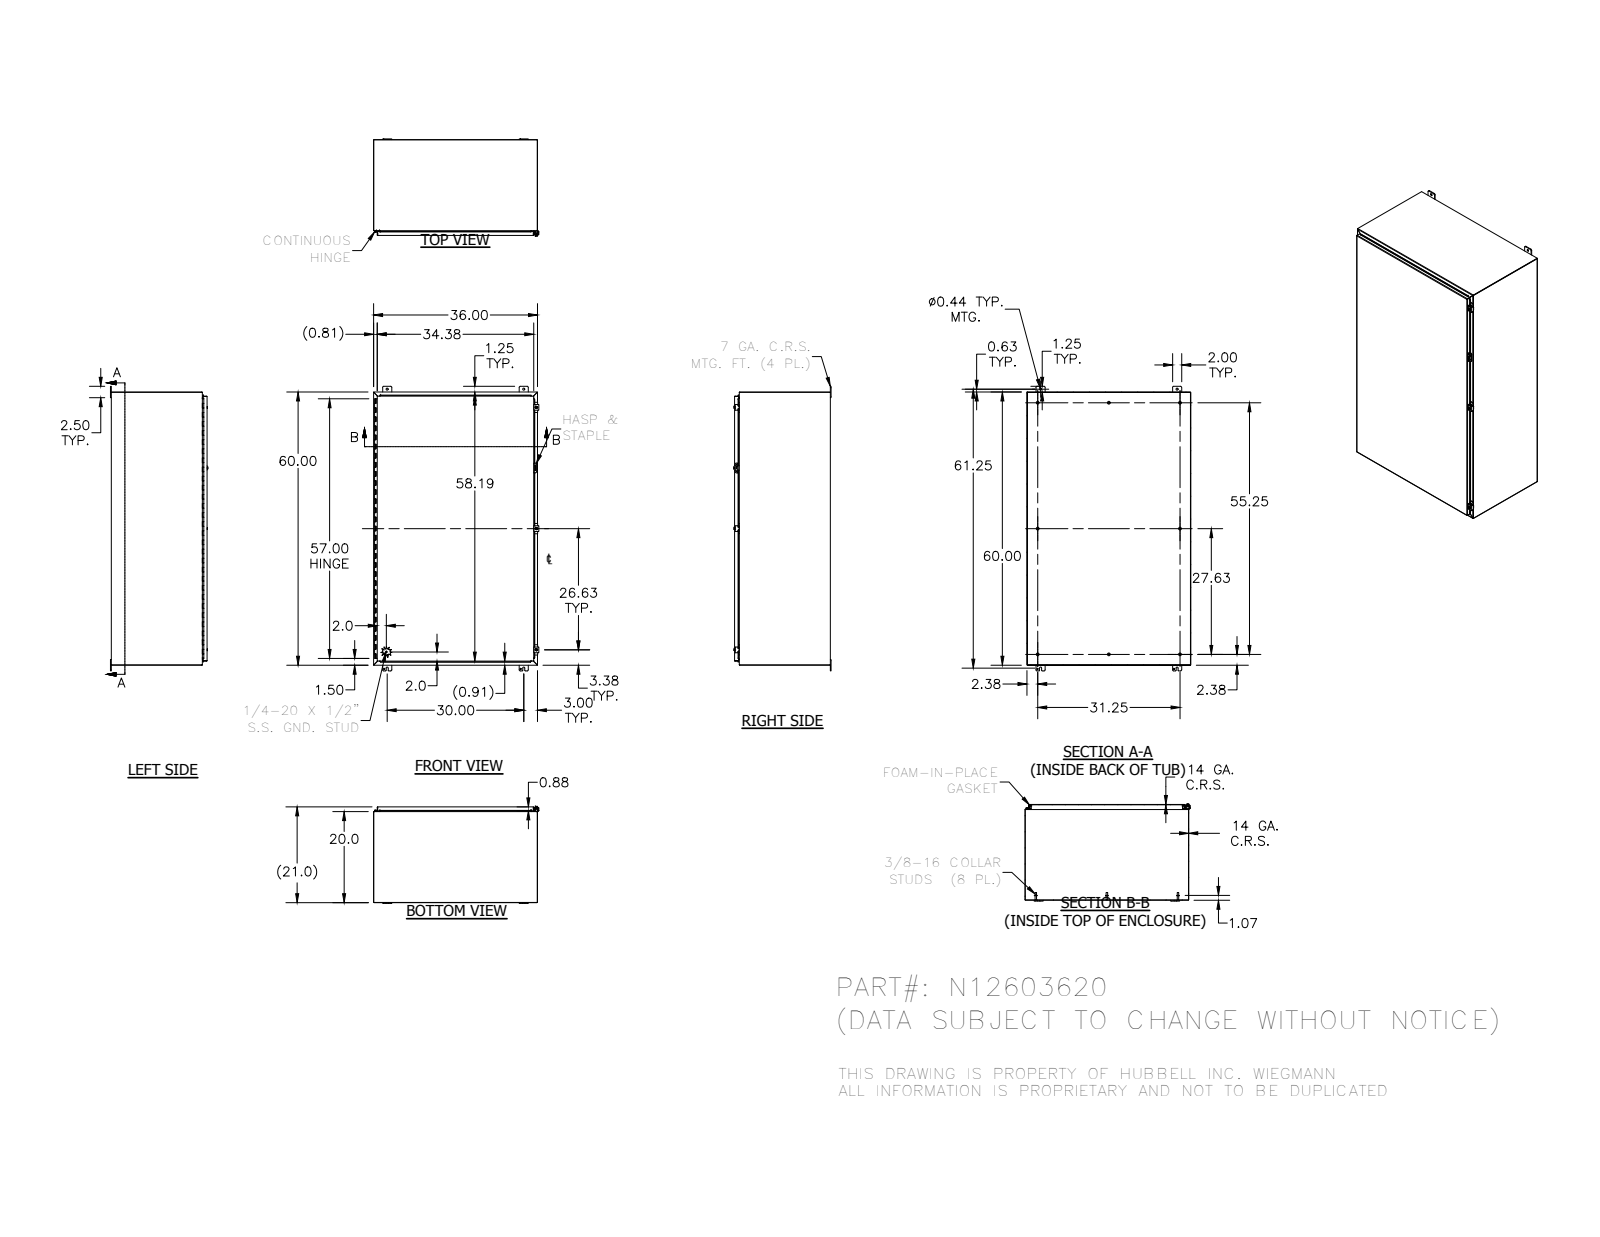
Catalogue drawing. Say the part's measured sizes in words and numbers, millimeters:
The part is named "N12603620; 34840; 38413; N123620TB (+8 more)". Its 3-D file was written by "Autodesk Inventor 2012 (AUTOMOTIVE_DESIGN)". It is 38 solids with 1357 faces: 806 planar, 428 cylindrical and 123 other. Overall it measures 1587.5 by 922.3 by 543.8 millimeters. Its volume is 10 930 000 cubic millimeters and its surface area 11 460 000 square millimeters. Round holes: 4 of diameter 8, 4 of diameter 11.1, 3 of diameter 2.8, 3 of diameter 5.4, 3 of diameter 7.1, 3 of diameter 7.6, 1 of diameter 3.2, 1 of diameter 4, 1 of diameter 12.7. Round bosses or shafts: 8 of diameter 15.9, 8 of diameter 8.4, 5 of diameter 6.4, 3 of diameter 13.2, 3 of diameter 12.7, 3 of diameter 8.9, 1 of diameter 8.6, 1 of diameter 3. Partial cylindrical surfaces (rounded edges, fillets, slot ends): 39 of radius 0.8, 27 of radius 3.2, 27 of radius 6.4, 21 of radius 0.8, 21 of radius 2.7, 15 of radius 1.6, 6 of radius 2.5, 6 of radius 3.6. The main face-to-face distances are 1.9, 532.4, 912.5, 530.5, 534.2, 1522.1, 910.6, 914.4, 1520.2, 1524. The hole center spacings are 40.5, 762, 1524, 1703.9, 20.1, 338.5, 745.4, 780.3.
